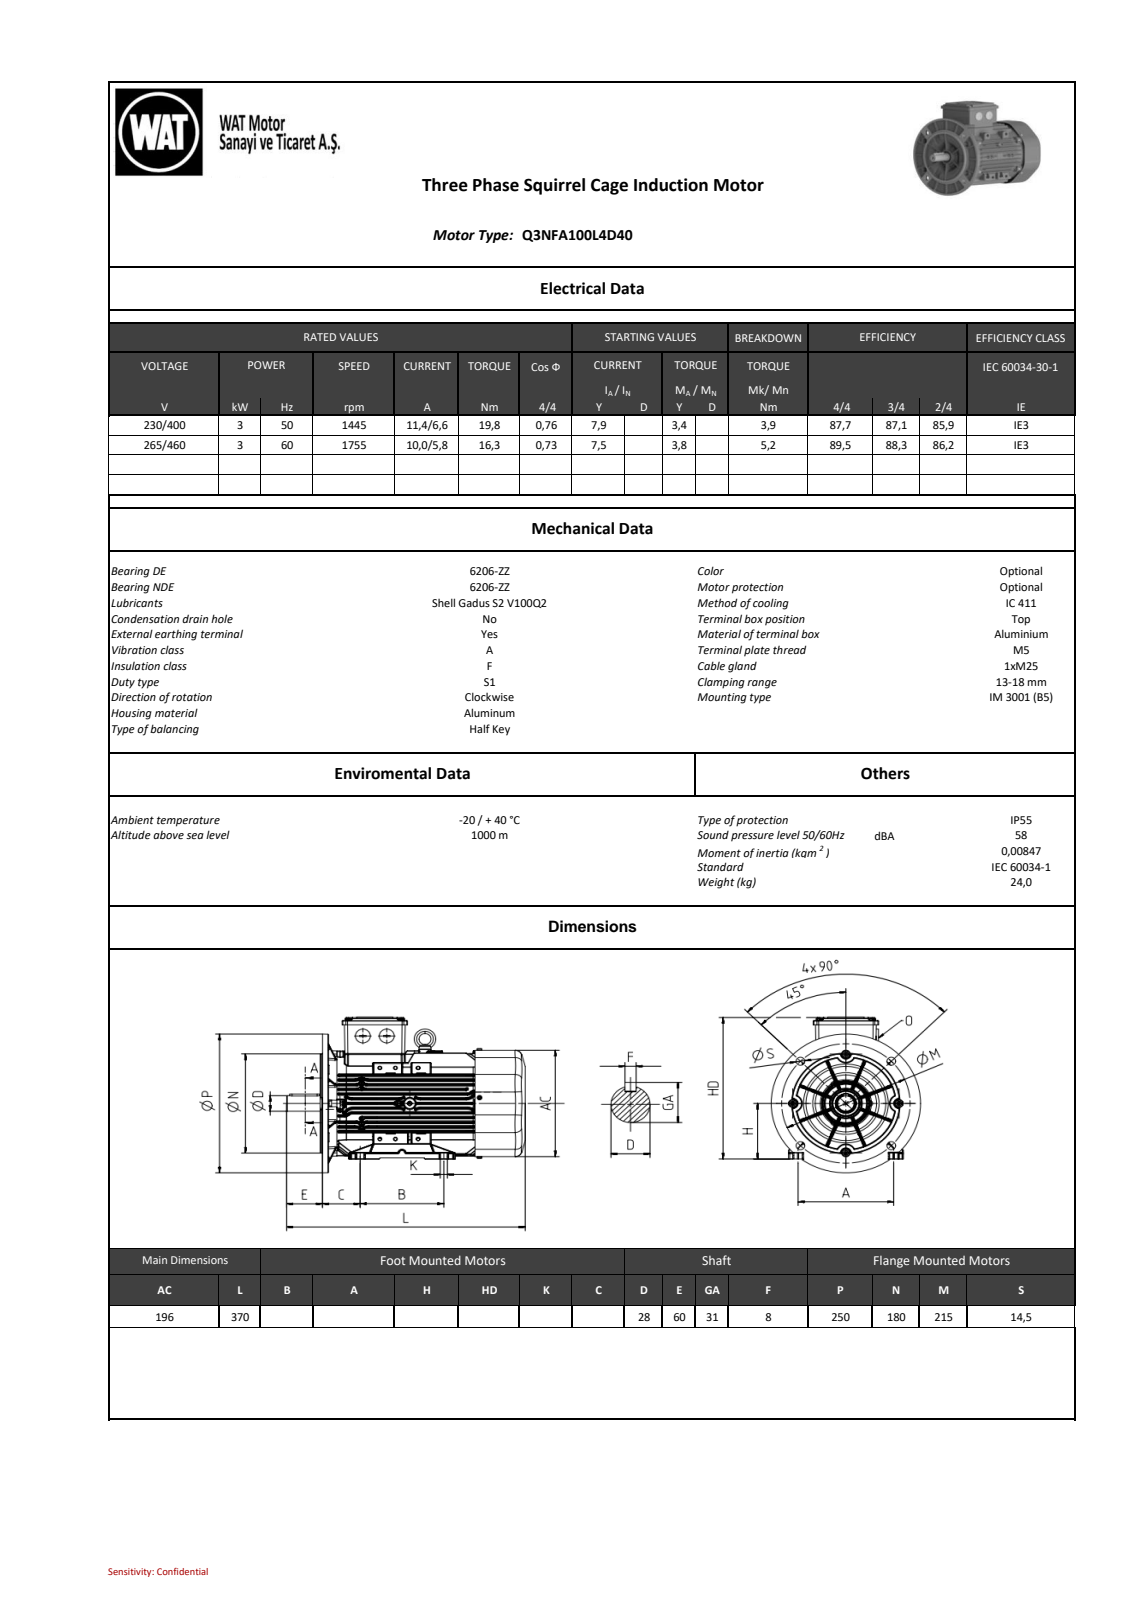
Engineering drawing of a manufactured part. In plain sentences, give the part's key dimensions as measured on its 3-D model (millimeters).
The part is named "C90127E0127Fj8s1". Its 3-D file was written by "SIEMENS PLM Software NX 11.0 (AUTOMOTIVE_DESIGN)". It is 0 solids with 15782 faces: 3329 planar, 5341 cylindrical and 7112 other. Overall it measures 370 by 254.96 by 248.92 millimeters. Round holes: 6 of diameter 5, 6 of diameter 6.5, 2 of diameter 2, 2 of diameter 2.5, 2 of diameter 3, 2 of diameter 12, 2 of diameter 25, 1 of diameter 4, 1 of diameter 8.5, 1 of diameter 10.5, 1 of diameter 28.6, 1 of diameter 32.94. Round bosses or shafts: 7 of diameter 8, 7 of diameter 4, 6 of diameter 11.8, 6 of diameter 10, 6 of diameter 6, 2 of diameter 35, 2 of diameter 27.8, 2 of diameter 25.25. Partial cylindrical surfaces (rounded edges, fillets, slot ends): 1761 of radius 0.5, 610 of radius 0.75, 458 of radius 0.8, 195 of radius 1, 144 of radius 0.25, 132 of radius 1.5, 99 of radius 4, 67 of radius 2. The main face-to-face distances are 0.8, 6, 2, 13.2, 14, 7.2, 41, 269, 296, 303.2. The hole center spacings are 92, 39, 96.14, 156.89, 184, 12.13, 14.13, 17.07.
